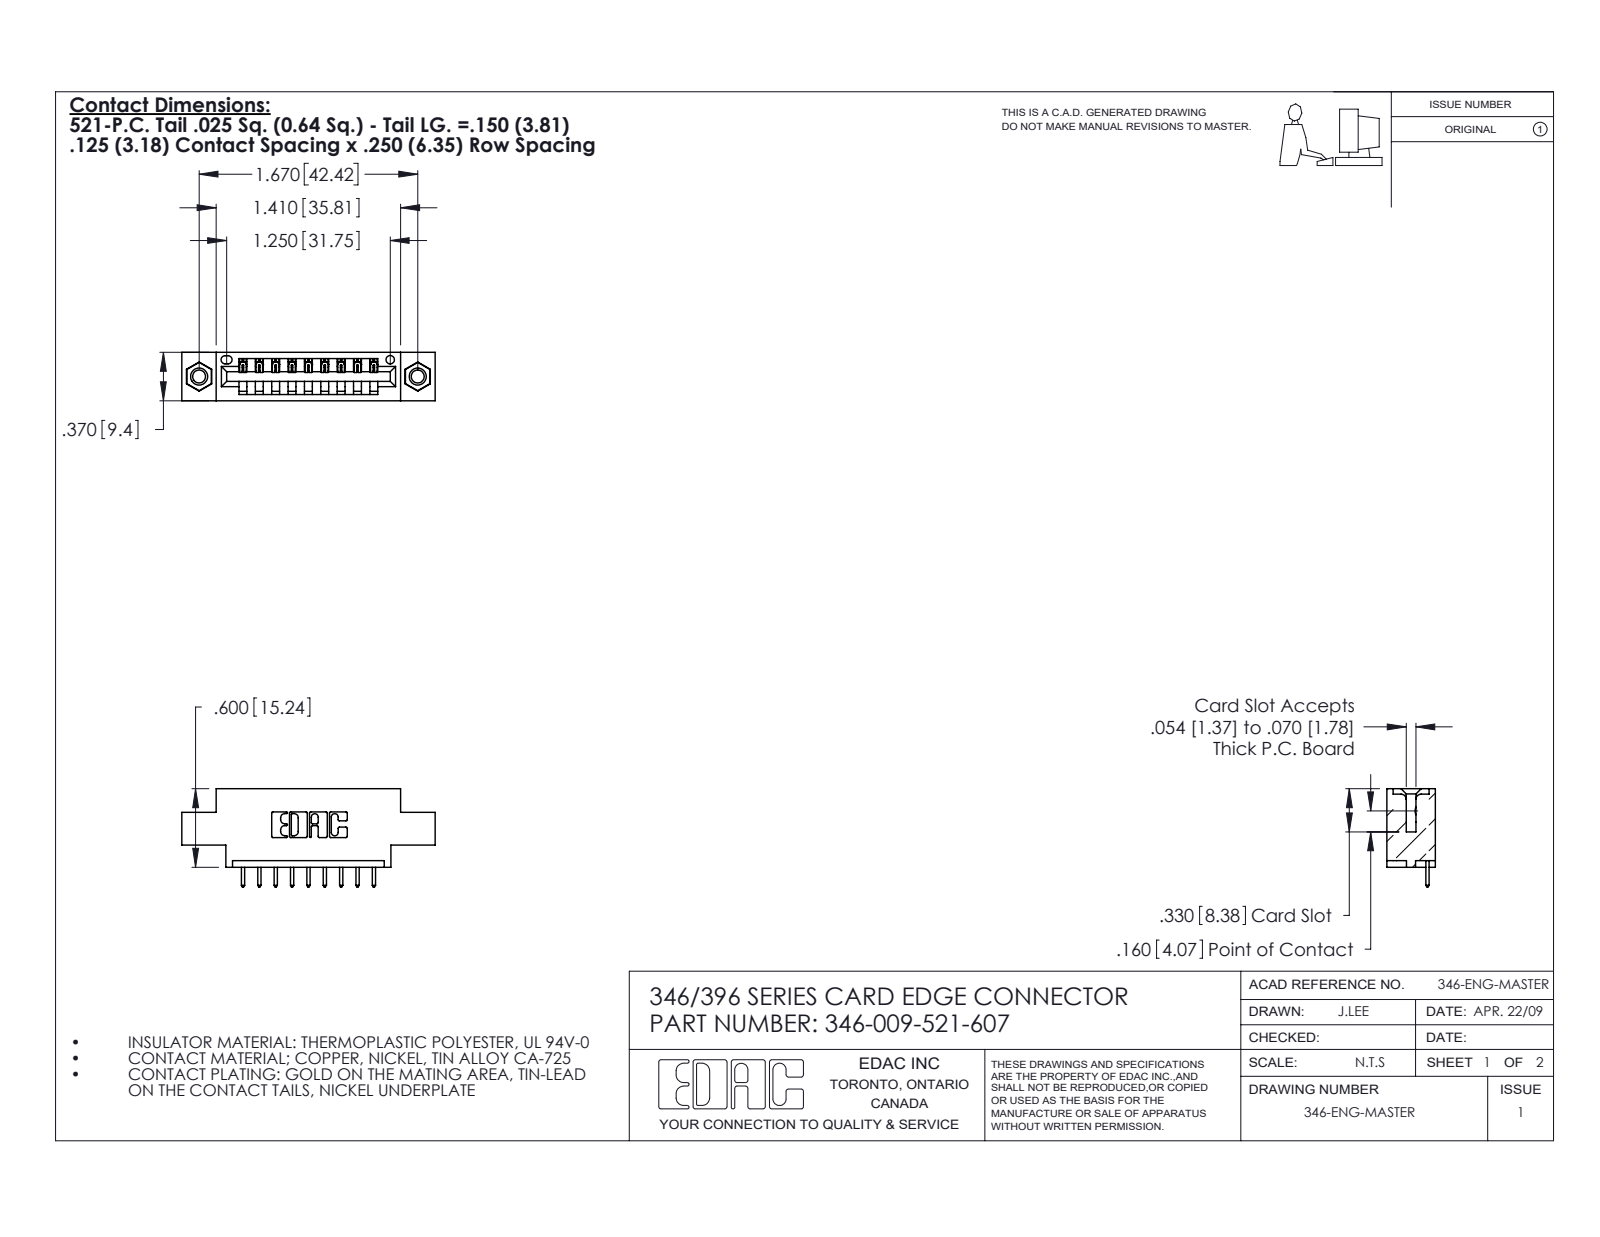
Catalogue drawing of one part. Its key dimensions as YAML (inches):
part_name: "346 Part_0.170 Offset - 0.156 Dia-TI; 345-292-001_345-293-121; 345-250-001_345-250-005-103; 346-009-521-607"
step_written_by: "SolidWorks 2020 (CONFIG_CONTROL_DESIGN)"
units: inches
bodies: {solids: 12, faces: 708, planar: 472, cylindrical: 220, other: 16}
overall_size: [1.935, 0.75, 0.37]
volume: 0.261
surface_area: 7.891
round_holes:
  - {diameter: 0.098, count: 2}
  - {diameter: 0.125, count: 2}
  - {diameter: 0.156, count: 2}
  - {diameter: 0.064, count: 1}
round_bosses_or_shafts:
  - {diameter: 0.155, count: 2}
partial_cylinders:
  - {radius: 0.01, count: 22}
  - {radius: 0.006, count: 18}
  - {radius: 0.01, count: 18}
  - {radius: 0.007, count: 6}
  - {radius: 0.031, count: 6}
  - {radius: 0.026, count: 3}
  - {radius: 0.031, count: 2}
  - {radius: 0.04, count: 2}
face_to_face_distances: [0.25, 0.37, 0.048, 0.322, 0.222, 0.148, 0.1, 0.174, 0.072, 0.298]
hole_center_spacings: [0.246, 1.465, 1.67]
